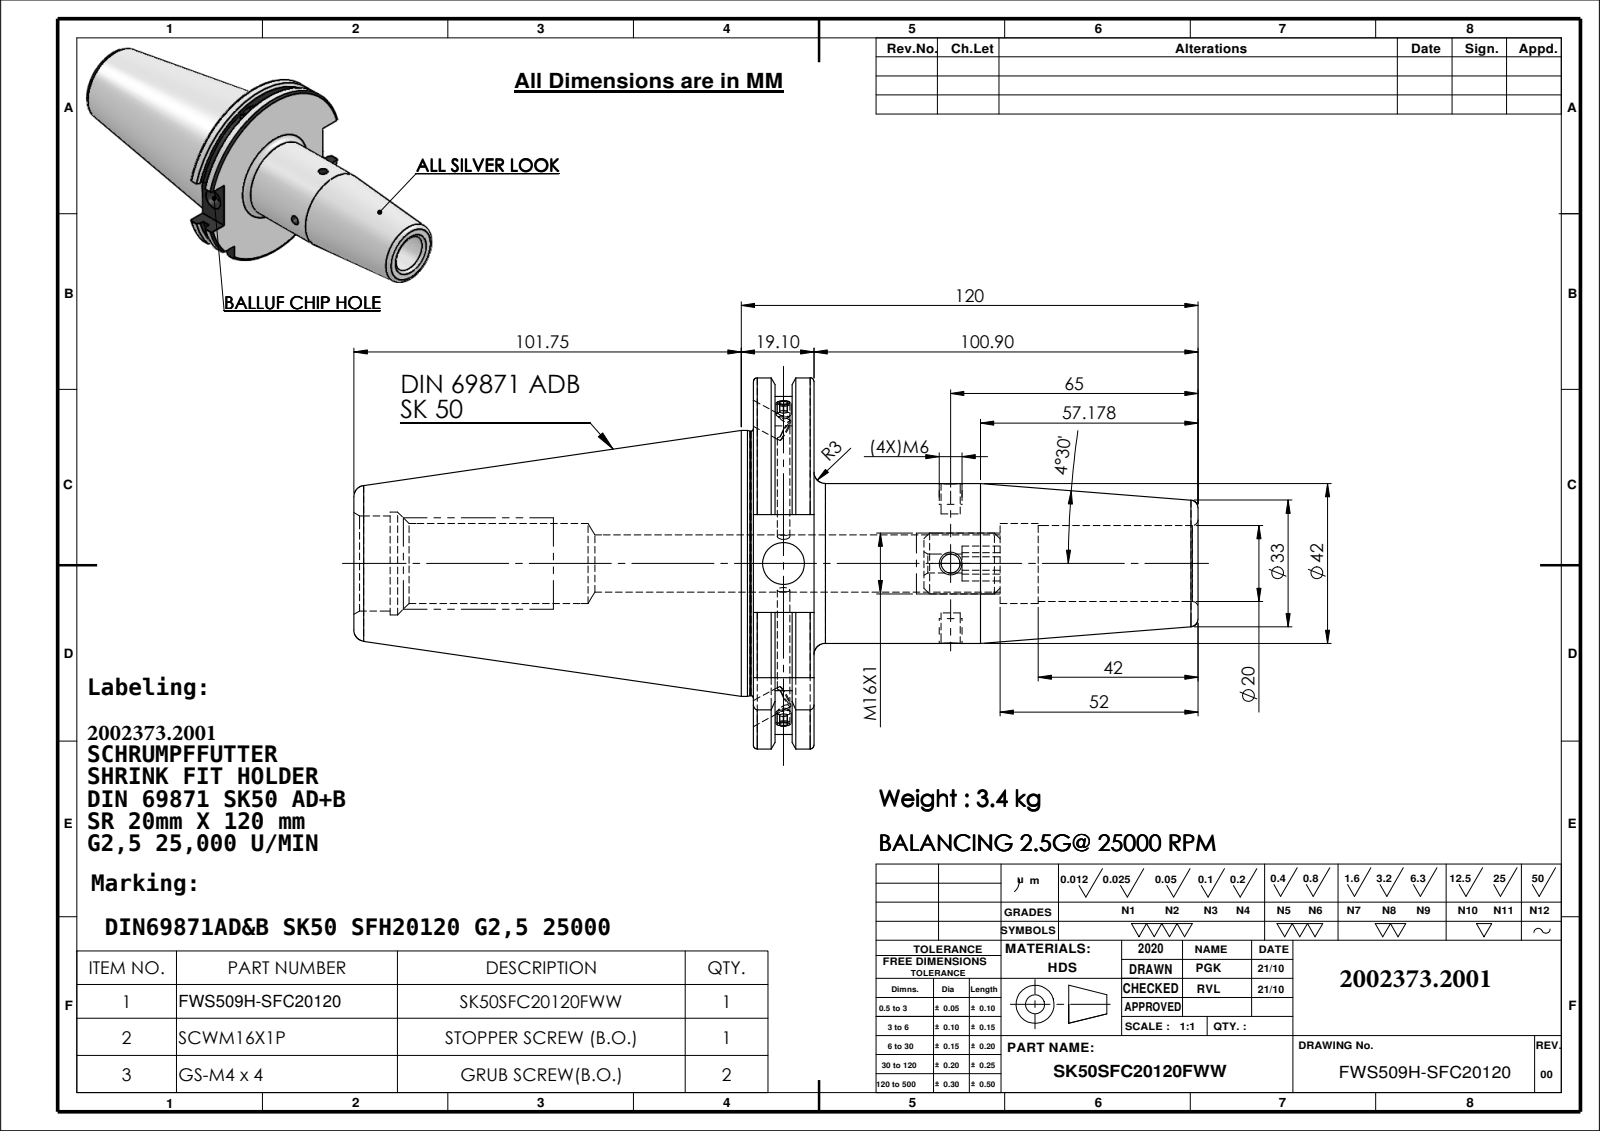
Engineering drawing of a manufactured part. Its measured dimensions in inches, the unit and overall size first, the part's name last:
Units: inches
Overall size (bounding box): 8.73 × 3.839 × 3.703
Round holes (diameter × count): ⌀0.197 ×2, ⌀0.236 ×2, ⌀0.13 ×1, ⌀0.433 ×1, ⌀0.591 ×1, ⌀0.787 ×1, ⌀0.827 ×1, ⌀0.984 ×1, ⌀1.063 ×1
Round bosses / shafts (diameter × count): ⌀2.75 ×1, ⌀2.734 ×1, ⌀1.654 ×1
Partial cylindrical surfaces — rounded edges, fillets, slot ends (radius × count): R1.768 ×1, R1.919 ×1
Main face-to-face distances: 0.626, 0.223, 0.403, 0.399, 0.176, 0.227, 4.132, 4.355, 4.531, 4.758
Hole centre spacings: 1.728
Volume: 25.99 in³ · Surface area: 95.99 in²
Bodies: 1 solid, 122 faces (29 planar, 53 cylindrical, 40 other)
Part name (STEP PRODUCT): 91506-SR220120
STEP written by: SolidWorks 2018 (AUTOMOTIVE_DESIGN)
